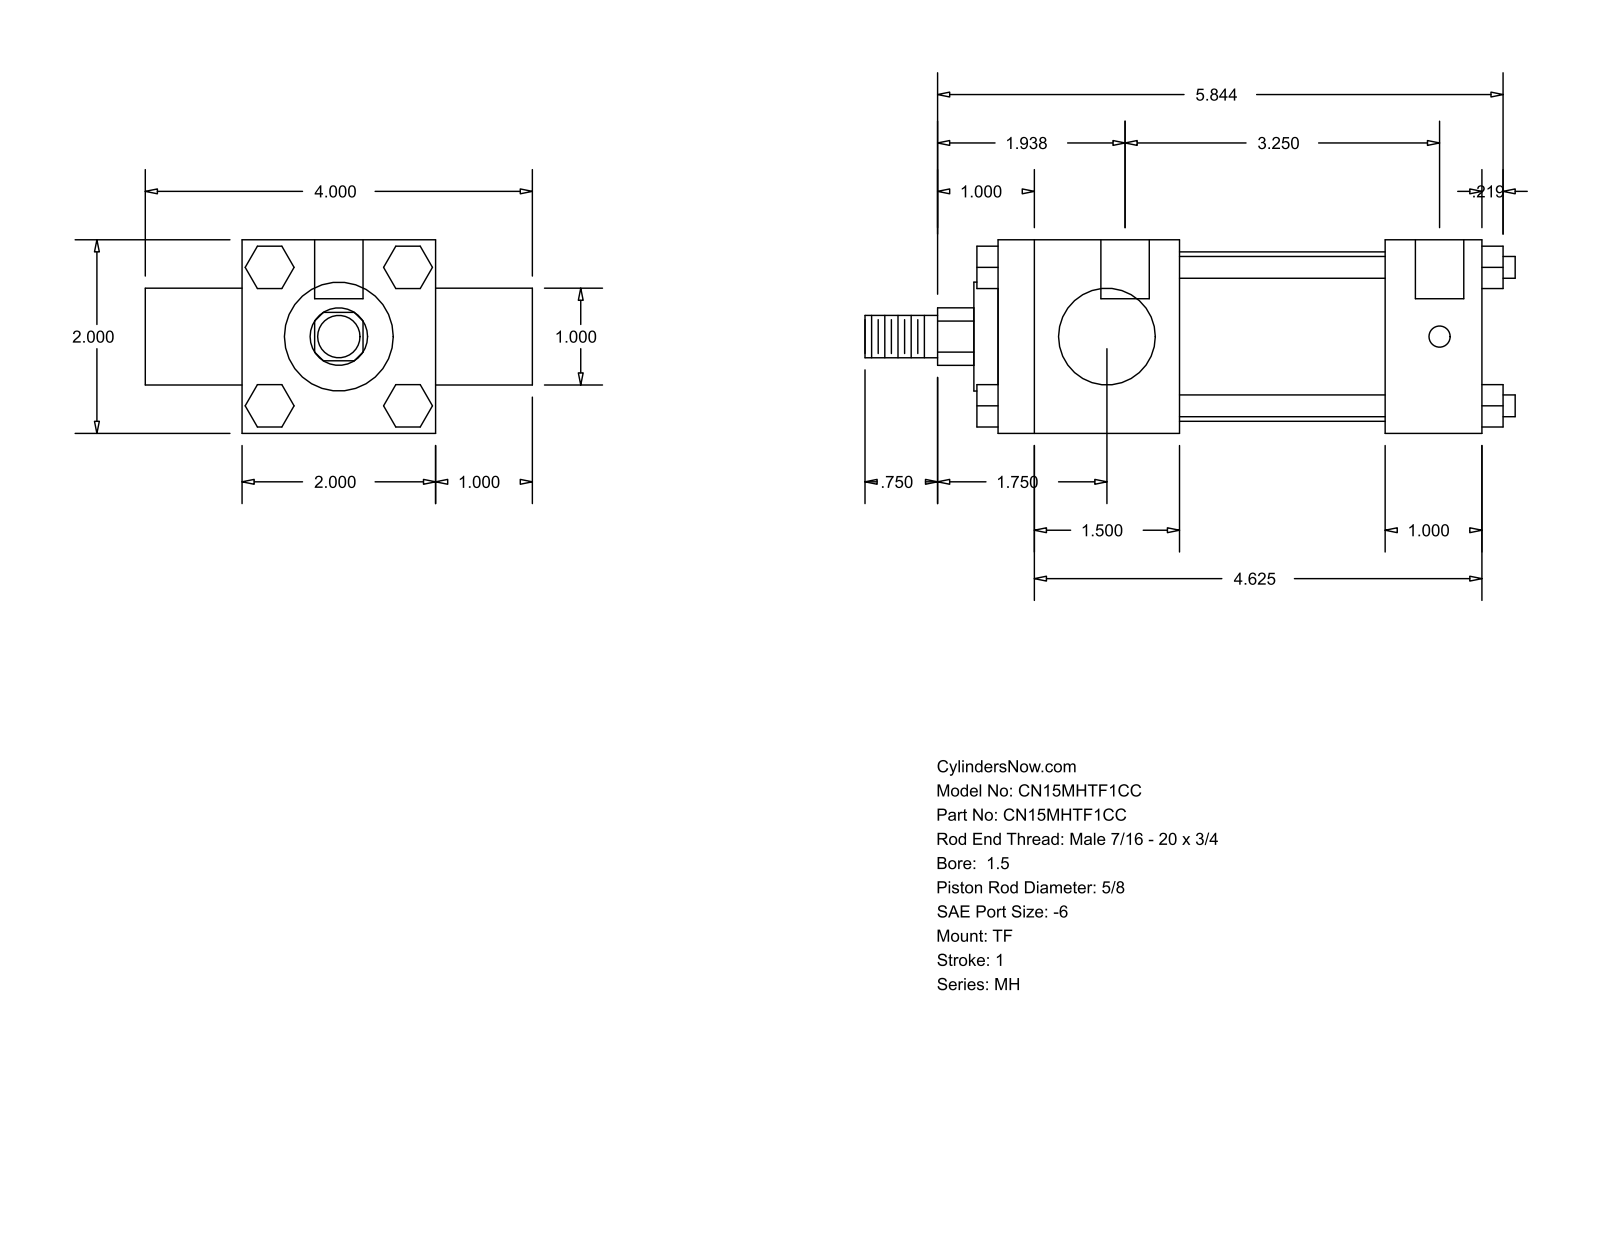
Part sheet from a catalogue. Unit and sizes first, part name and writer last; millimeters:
Units: millimetres
Overall size (bounding box): 170.66 × 101.6 × 50.8
Round holes (diameter × count): ⌀5.56 ×3, ⌀12.7 ×2
Round bosses / shafts (diameter × count): ⌀5.71 ×4, ⌀44.45 ×1, ⌀28.57 ×1, ⌀25.4 ×1, ⌀15.88 ×1, ⌀11.11 ×1
Partial cylindrical surfaces — rounded edges, fillets, slot ends (radius × count): R7.54 ×1
Main face-to-face distances: 50.8, 127, 53.97, 25.4, 76.2, 47.62, 79.38, 101.59, 25.41, 11.11
Hole centre spacings: 3.17, 82.55, 85.72
Bodies: 0 solids, 120 faces (92 planar, 28 cylindrical, 0 other)
Part name (STEP PRODUCT): MH_TF__0150_0.625
STEP written by: GSSL Pune (CONFIG_CONTROL_DESIGN)
